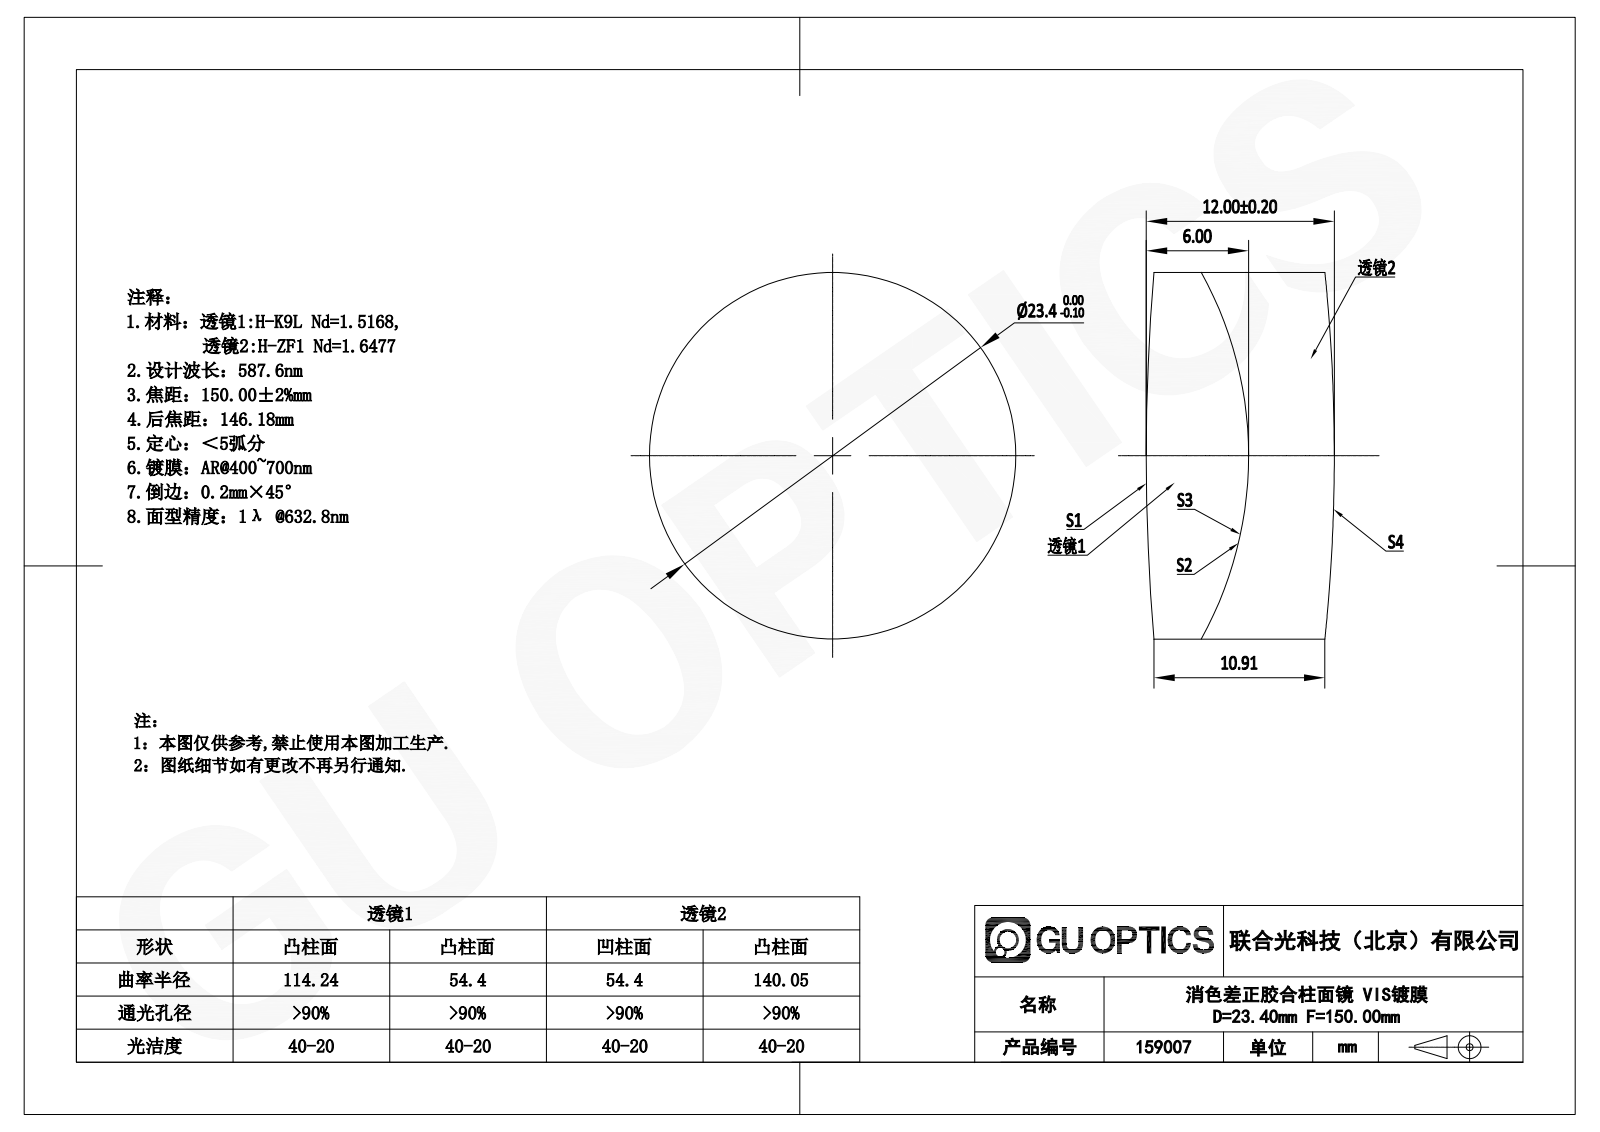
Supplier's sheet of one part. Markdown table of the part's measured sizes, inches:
| quantity | value |
| --- | --- |
| part name | 159007 |
| STEP written by | SolidWorks 2020 (CONFIG_CONTROL_DESIGN) |
| units | inches |
| bodies | 1 solid, 5 faces (0 planar, 5 cylindrical, 0 other) |
| overall size | 0.921 × 0.921 × 0.472 |
| volume | 0.308 in³ |
| surface area | 2.64 in² |
| round bosses / shafts (diameter × count) | 0.921 × 1 |
| partial cylindrical surfaces (radius × count) | 4.498 × 1, 5.531 × 1 |
